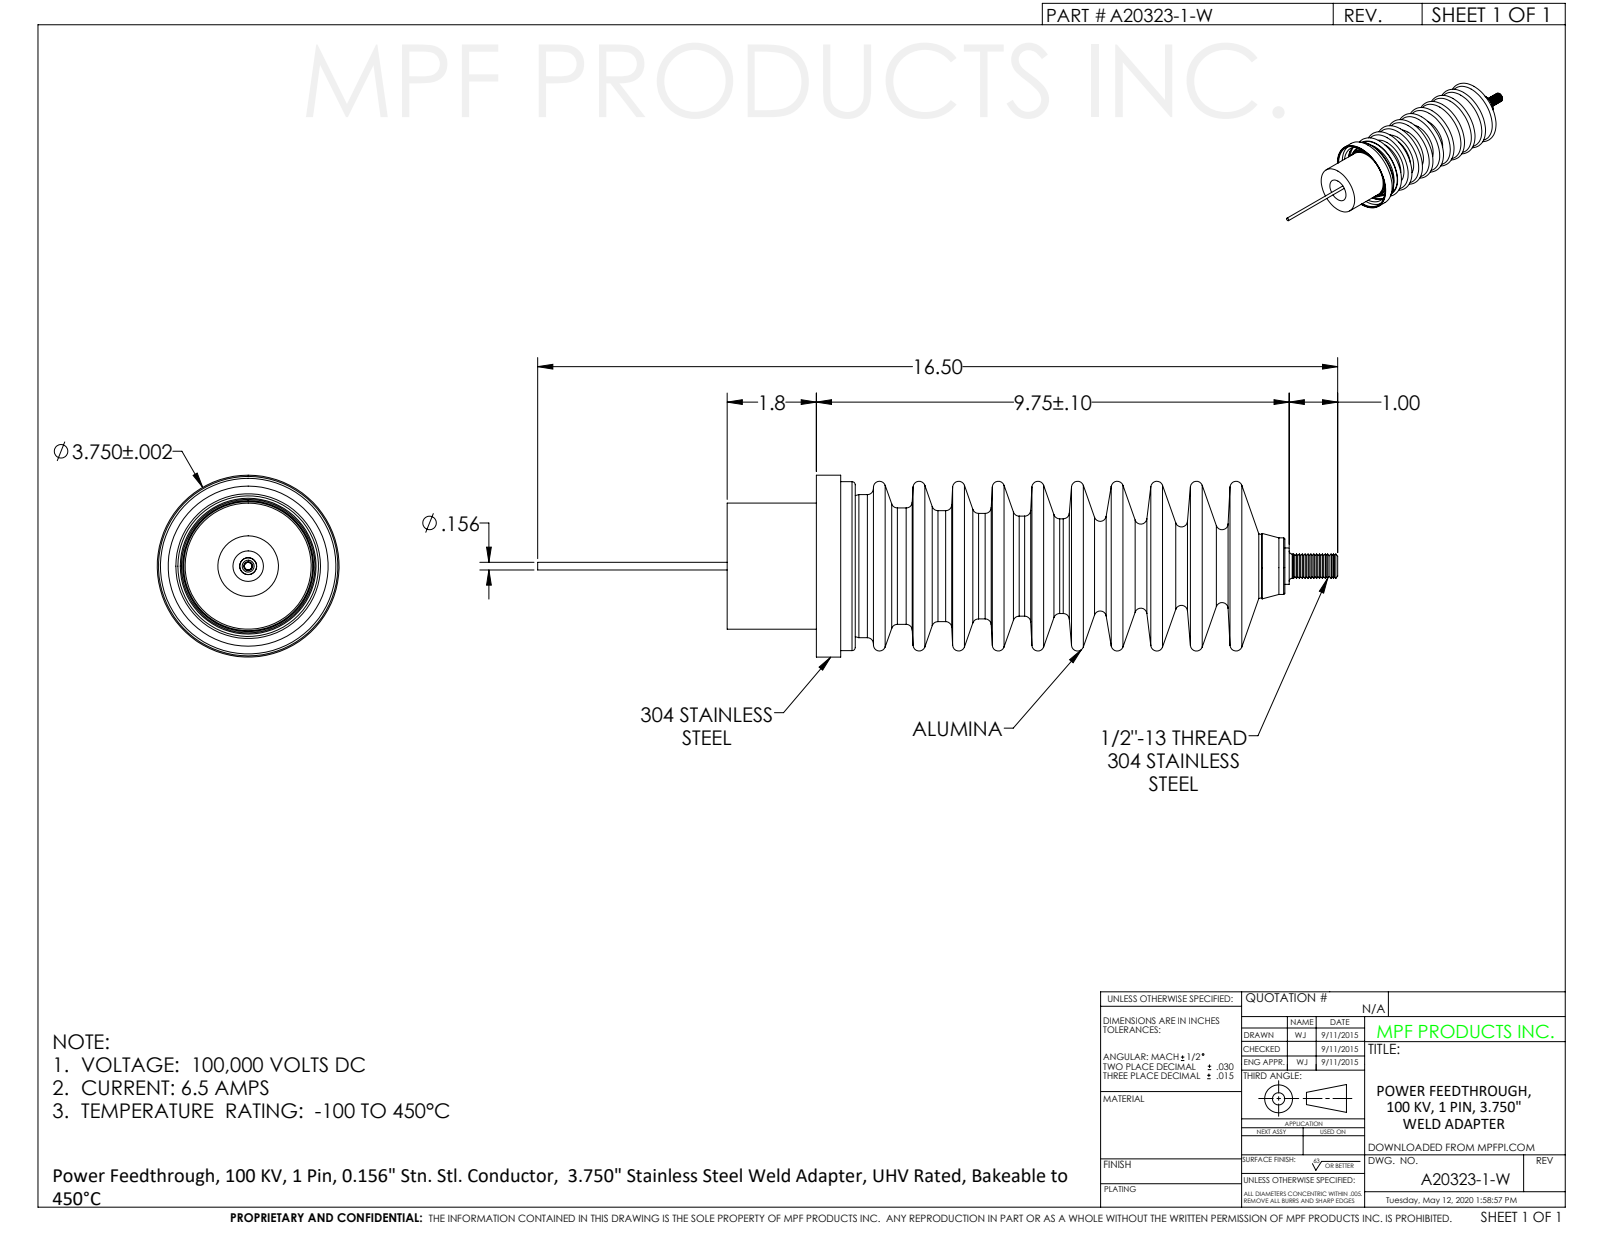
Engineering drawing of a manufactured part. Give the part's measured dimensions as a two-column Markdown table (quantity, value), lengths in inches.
| quantity | value |
| --- | --- |
| part name | A20323-1-W |
| STEP written by | SolidWorks 2020 (CONFIG_CONTROL_DESIGN) |
| units | inches |
| bodies | 1 solid, 238 faces (16 planar, 36 cylindrical, 186 other) |
| overall size | 16.5 × 3.75 × 3.75 |
| volume | 57.36 in³ |
| surface area | 261 in² |
| round holes (diameter × count) | 1.25 × 1, 3.3 × 1, 3.433 × 1, 3.62 × 1, 3.7 × 1 |
| round bosses / shafts (diameter × count) | 3.75 × 1, 3.483 × 1, 3.4 × 1, 2.95 × 1, 2.6 × 1, 2.4 × 1, 2.287 × 1, 2.175 × 1 |
| main face-to-face distances | 2.64, 2.341, 0.299, 2.15, 0.191, 0.49, 2.34, 0.19, 0.3, 11.5 |
